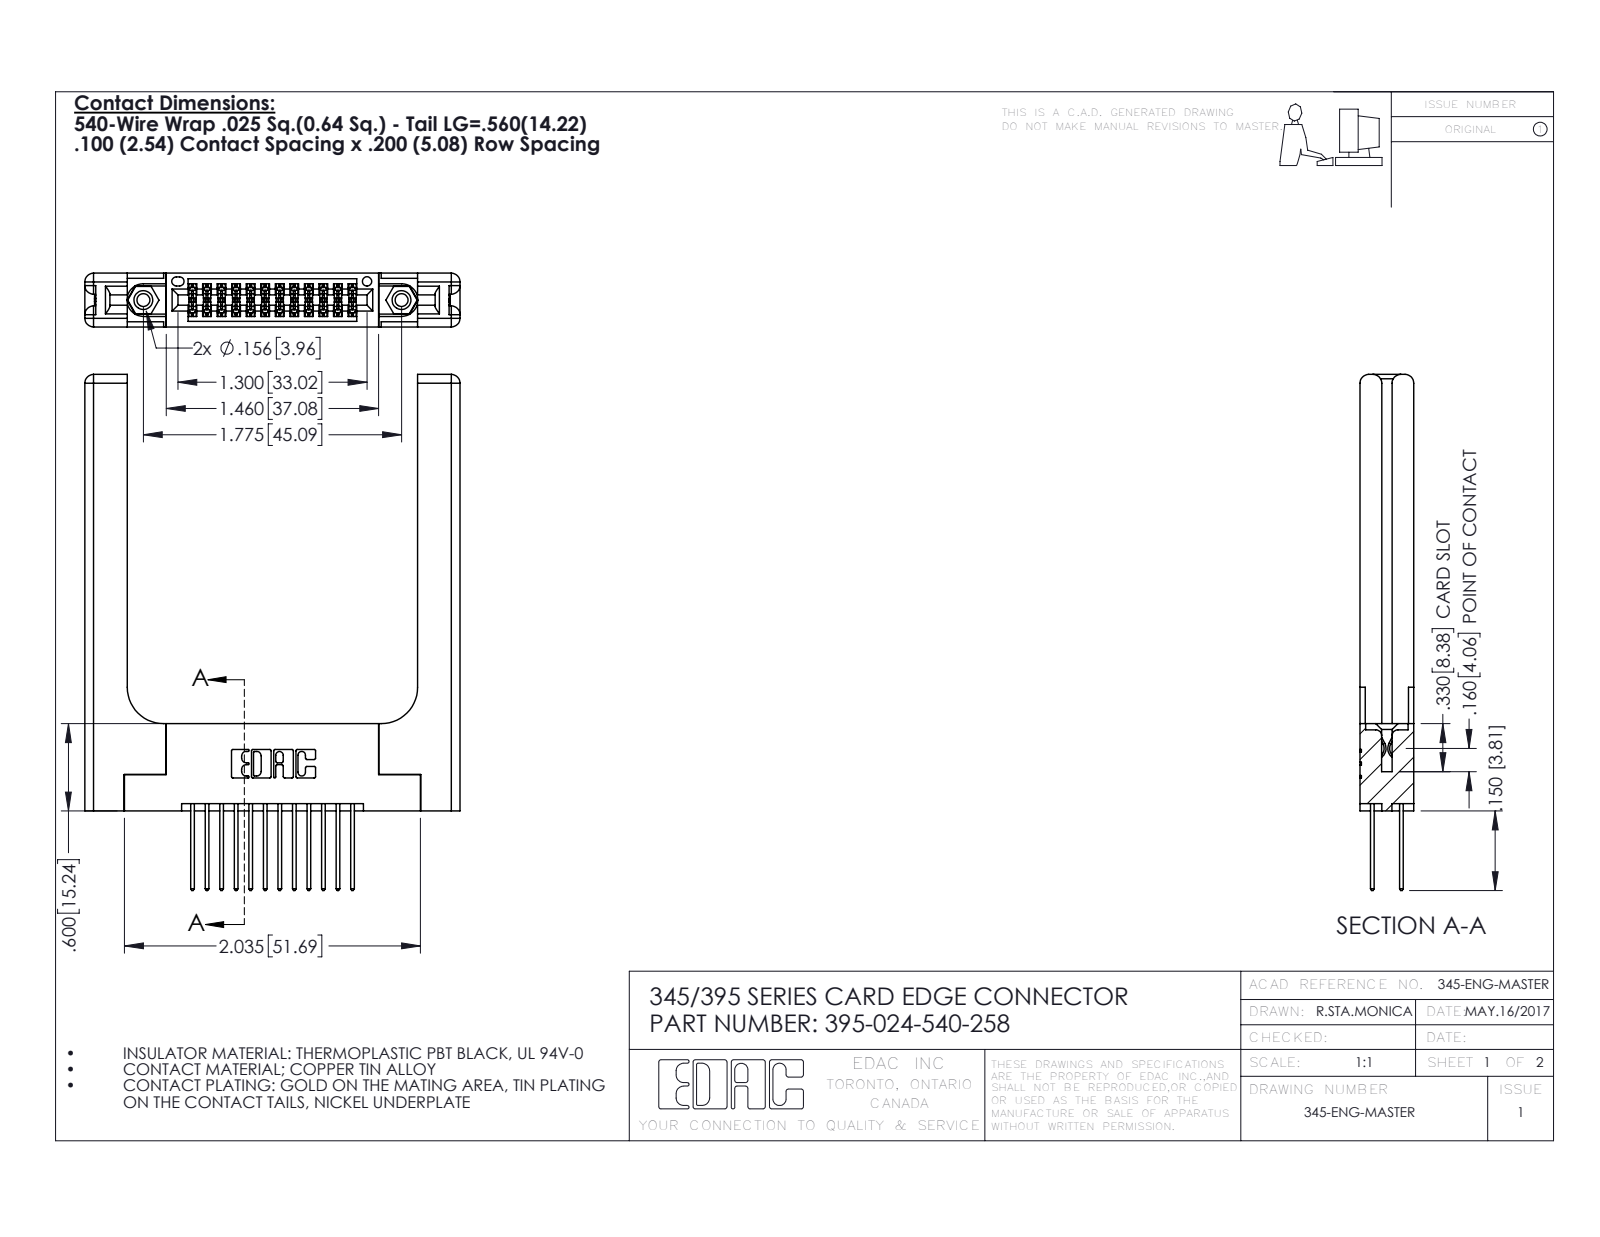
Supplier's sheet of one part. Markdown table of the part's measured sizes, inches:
| quantity | value |
| --- | --- |
| part name | 345-292-001_345-293-140; 345 Part_Flush Mounting Lugs - 0.156 Dia-TH; 395-024-540-258; 345-220-058_345-220-058 (+1 more) |
| STEP written by | SolidWorks 2016 (CONFIG_CONTROL_DESIGN) |
| units | inches |
| bodies | 29 solids, 1582 faces (1020 planar, 502 cylindrical, 60 other) |
| overall size | 3.547 × 2.579 × 0.37 |
| volume | 0.894 in³ |
| surface area | 21.74 in² |
| round holes (diameter × count) | 0.089 × 2, 0.125 × 2, 0.156 × 2, 0.064 × 1 |
| round bosses / shafts (diameter × count) | 0.155 × 2 |
| partial cylindrical surfaces (radius × count) | 0.006 × 36, 0.01 × 24, 0.01 × 22, 0.06 × 16, 0.007 × 6, 0.031 × 6, 0.026 × 3, 0.014 × 2 |
| main face-to-face distances | 0.37, 0.072, 0.298, 0.2, 0.077, 0.148, 0.15, 0.22, 0.098, 0.272 |
| hole center spacings | 0.27, 1.543, 1.775 |
